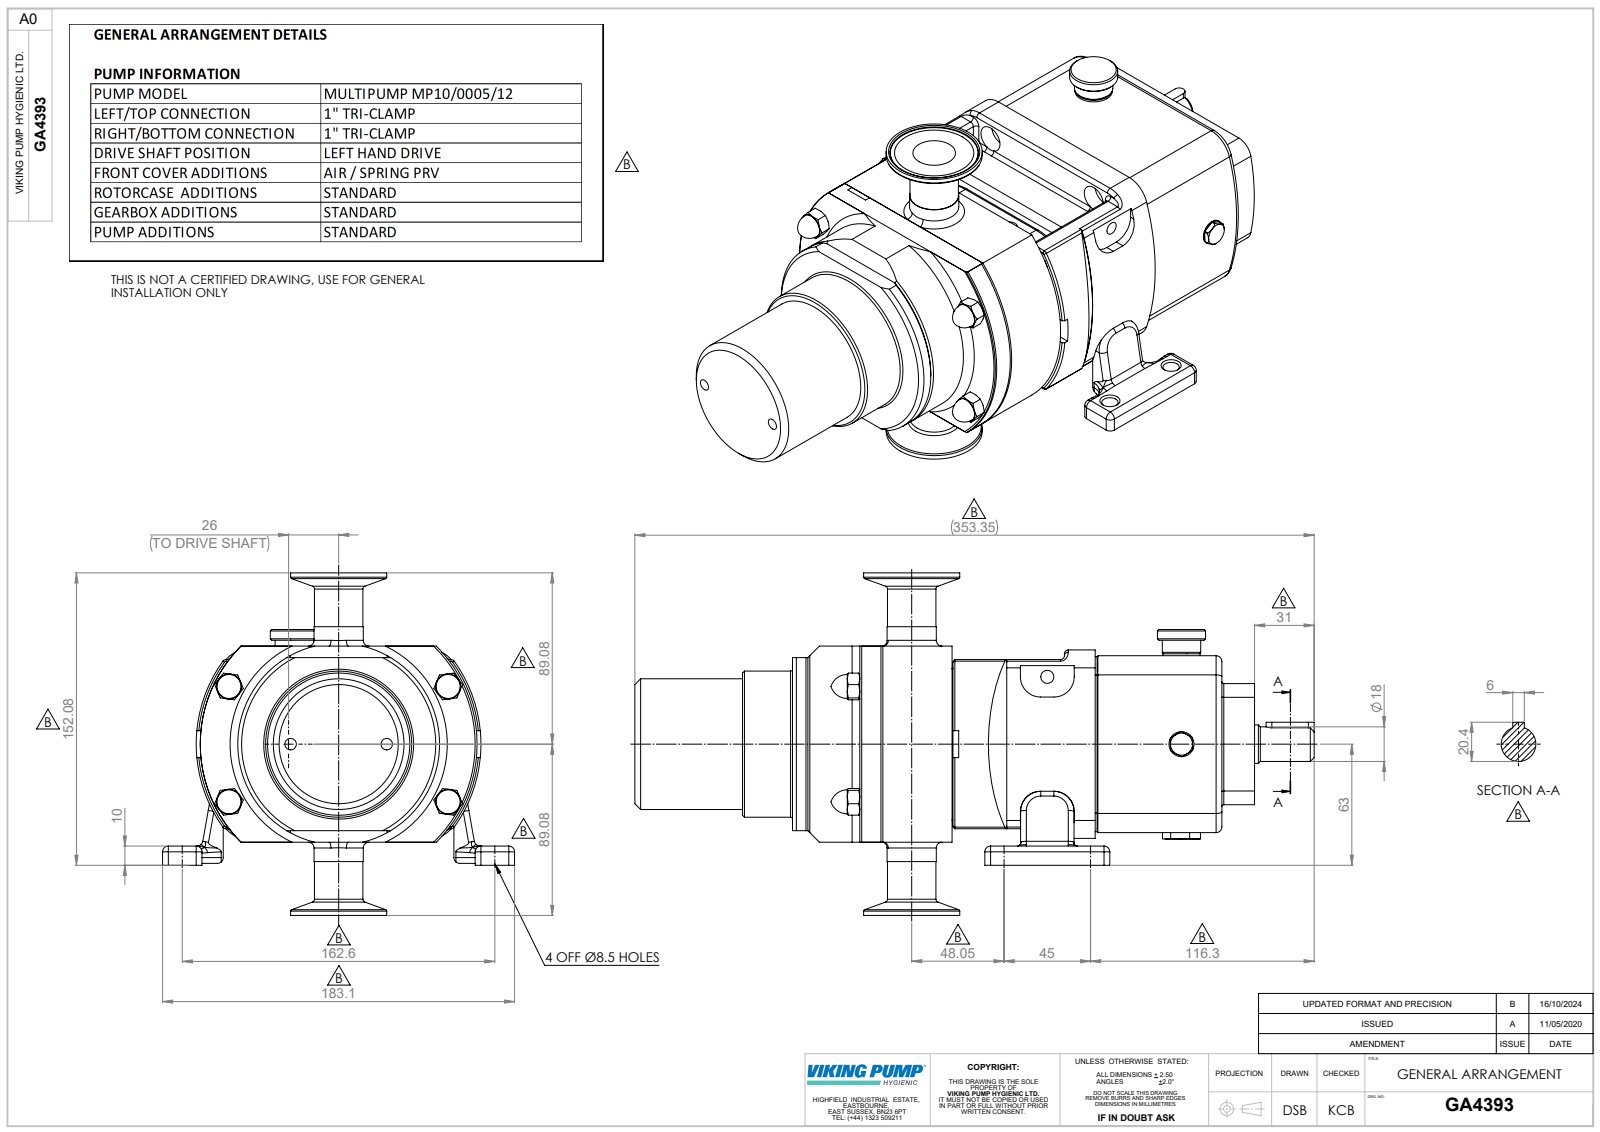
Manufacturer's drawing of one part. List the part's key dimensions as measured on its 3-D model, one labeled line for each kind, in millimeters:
Part name (STEP PRODUCT): GA4393; Copy of Z94-5121-11 - 1 INCH^GA4393; Copy of MP-CP10 SPRING PRV^GA4393; Copy of CP10-0005-12 V L^GA4393
STEP written by: SolidWorks 2023 (AUTOMOTIVE_DESIGN)
Units: millimetres
Bodies: 4 solids, 737 faces (234 planar, 230 cylindrical, 273 other)
Overall size (bounding box): 353.35 × 183.1 × 178.15
Volume: 3 031 000 mm³ · Surface area: 236 076 mm²
Round holes (diameter × count): ⌀8.5 ×4, ⌀14 ×4, ⌀6 ×2, ⌀7.63 ×2, ⌀6.8 ×1, ⌀22.2 ×1, ⌀22.53 ×1
Round bosses / shafts (diameter × count): ⌀30 ×2, ⌀105 ×1, ⌀76 ×1, ⌀68 ×1, ⌀50 ×1, ⌀25.6 ×1, ⌀25.2 ×1, ⌀25.02 ×1
Partial cylindrical surfaces — rounded edges, fillets, slot ends (radius × count): R2 ×32, R3 ×32, R13.5 ×12, R3.5 ×6, R10.5 ×6, R5.5 ×4, R6 ×4, R9 ×4
Main face-to-face distances: 12, 102, 193.35, 205.35, 92, 4.99, 97.01, 96.99, 5.01, 124
Hole centre spacings: 40.63, 40.66, 45, 73.79, 73.89, 76, 77.02, 108.2
